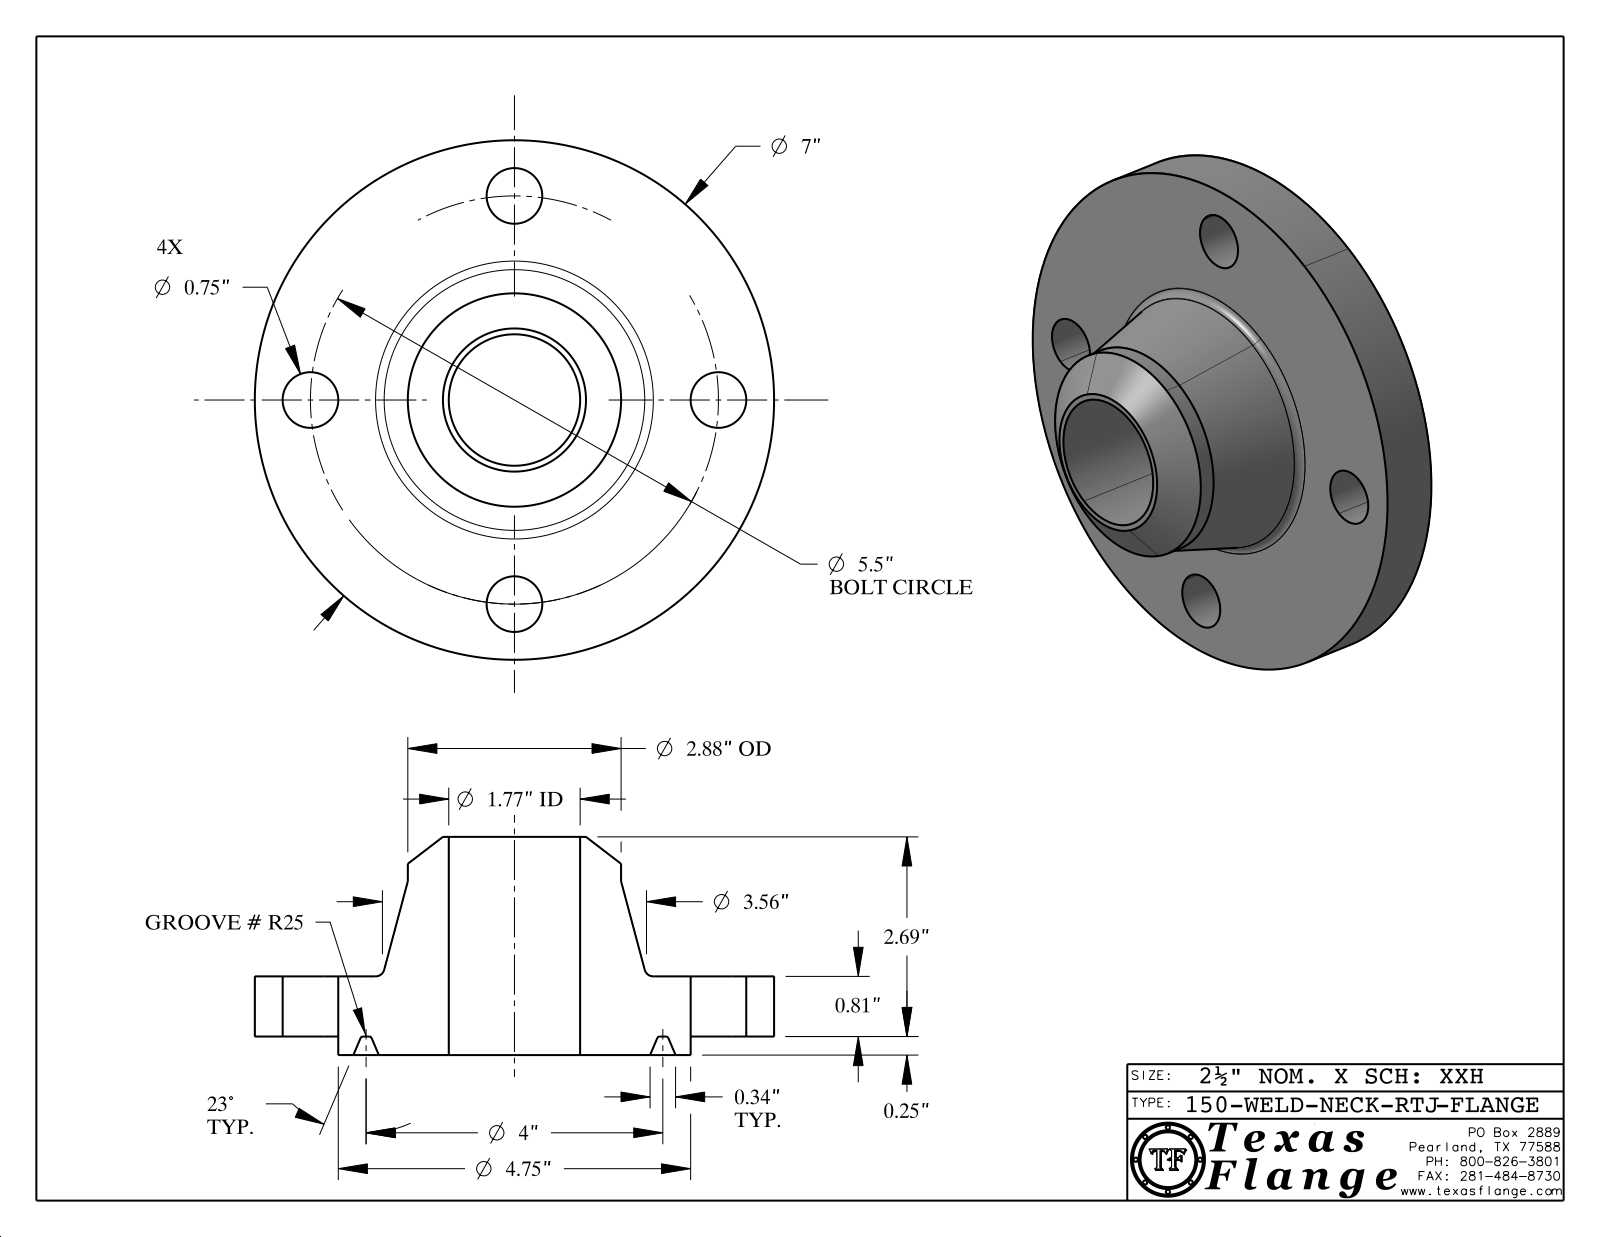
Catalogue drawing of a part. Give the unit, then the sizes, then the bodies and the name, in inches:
Units: inches
Overall size (bounding box): 7 × 7 × 2.94
Round holes (diameter × count): ⌀0.75 ×4, ⌀0.495 ×1, ⌀1.771 ×1
Round bosses / shafts (diameter × count): ⌀0.03 ×8, ⌀7 ×1, ⌀4.75 ×1, ⌀2.875 ×1, ⌀0.39 ×1
Main face-to-face distances: 0.81, 0.25, 1.06, 2.94, 2.69, 1.88, 1.055, 0.805, 1.885, 0.148
Hole centre spacings: 2.75, 3.889, 2.105, 5.081, 5.5
Volume: 39.85 in³ · Surface area: 130.8 in²
Bodies: 1 solid, 421 faces (371 planar, 36 cylindrical, 14 other)
Part name (STEP PRODUCT): 150-WELD-NECK-RTJ
STEP written by: CATIA V5 STEP AP214 (AUTOMOTIVE_DESIGN)
